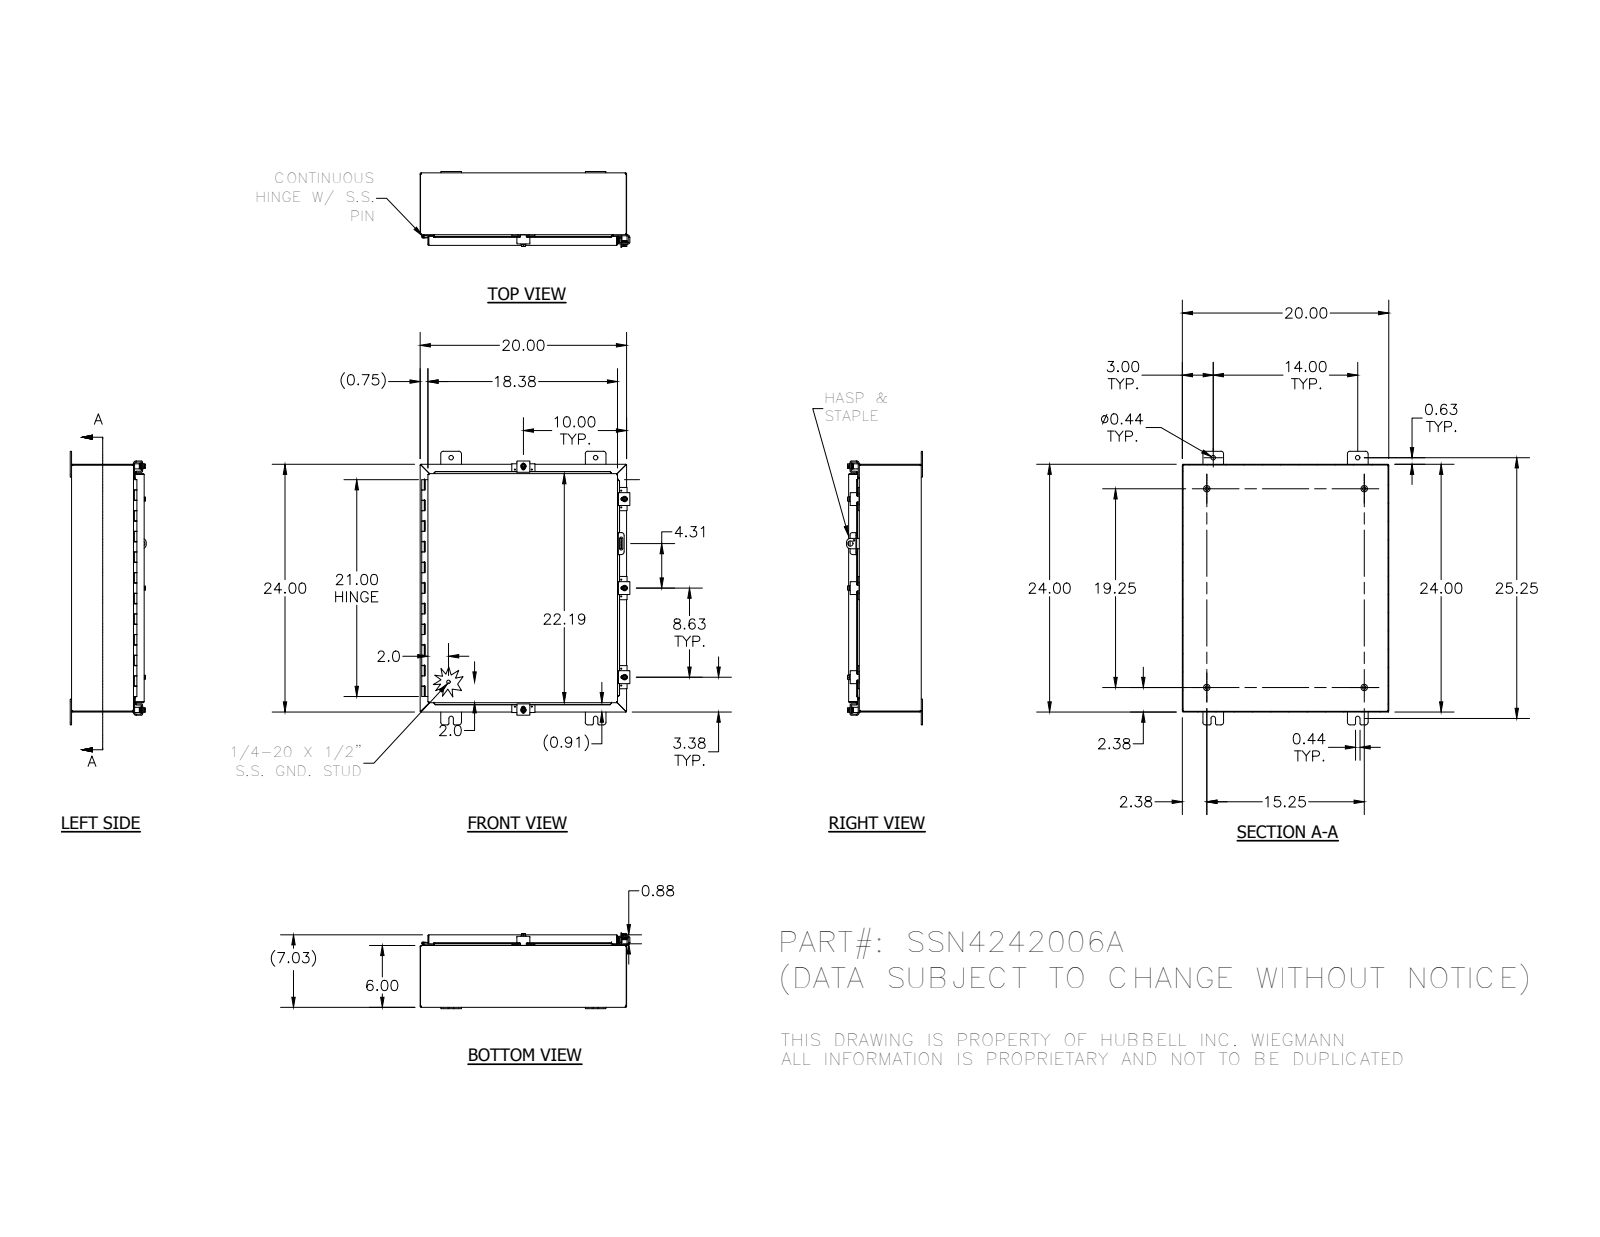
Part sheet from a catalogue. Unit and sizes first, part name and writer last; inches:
Units: inches
Overall size (bounding box): 26.5 × 20.216 × 7.355
Round holes (diameter × count): ⌀0.11 ×10, ⌀0.211 ×5, ⌀0.281 ×5, ⌀0.3 ×5, ⌀0.438 ×4, ⌀0.125 ×1, ⌀0.156 ×1, ⌀0.5 ×1
Round bosses / shafts (diameter × count): ⌀0.25 ×7, ⌀0.52 ×5, ⌀0.5 ×5, ⌀0.35 ×5, ⌀0.625 ×4, ⌀0.33 ×4, ⌀0.337 ×1, ⌀0.12 ×1
Partial cylindrical surfaces — rounded edges, fillets, slot ends (radius × count): R0.03 ×61, R0.125 ×35, R0.25 ×31, R0.031 ×23, R0.105 ×23, R0.062 ×16, R0.141 ×10, R0.07 ×8
Main face-to-face distances: 0.074, 6.959, 6.885, 7.033, 19.926, 23.926, 5.926, 1.033, 20, 19.852
Hole centre spacings: 0.876, 23.303, 1.625, 7.82, 8.625, 8.625, 9.443, 17.25
Volume: 140 in³ · Surface area: 3 658 in²
Bodies: 42 solids, 1656 faces (660 planar, 713 cylindrical, 283 other)
Part name (STEP PRODUCT): SSN4242006ABKP; SSN4242006A; 30824-1; 32874-24P (+8 more)
STEP written by: SolidWorks 2014 (AUTOMOTIVE_DESIGN)
